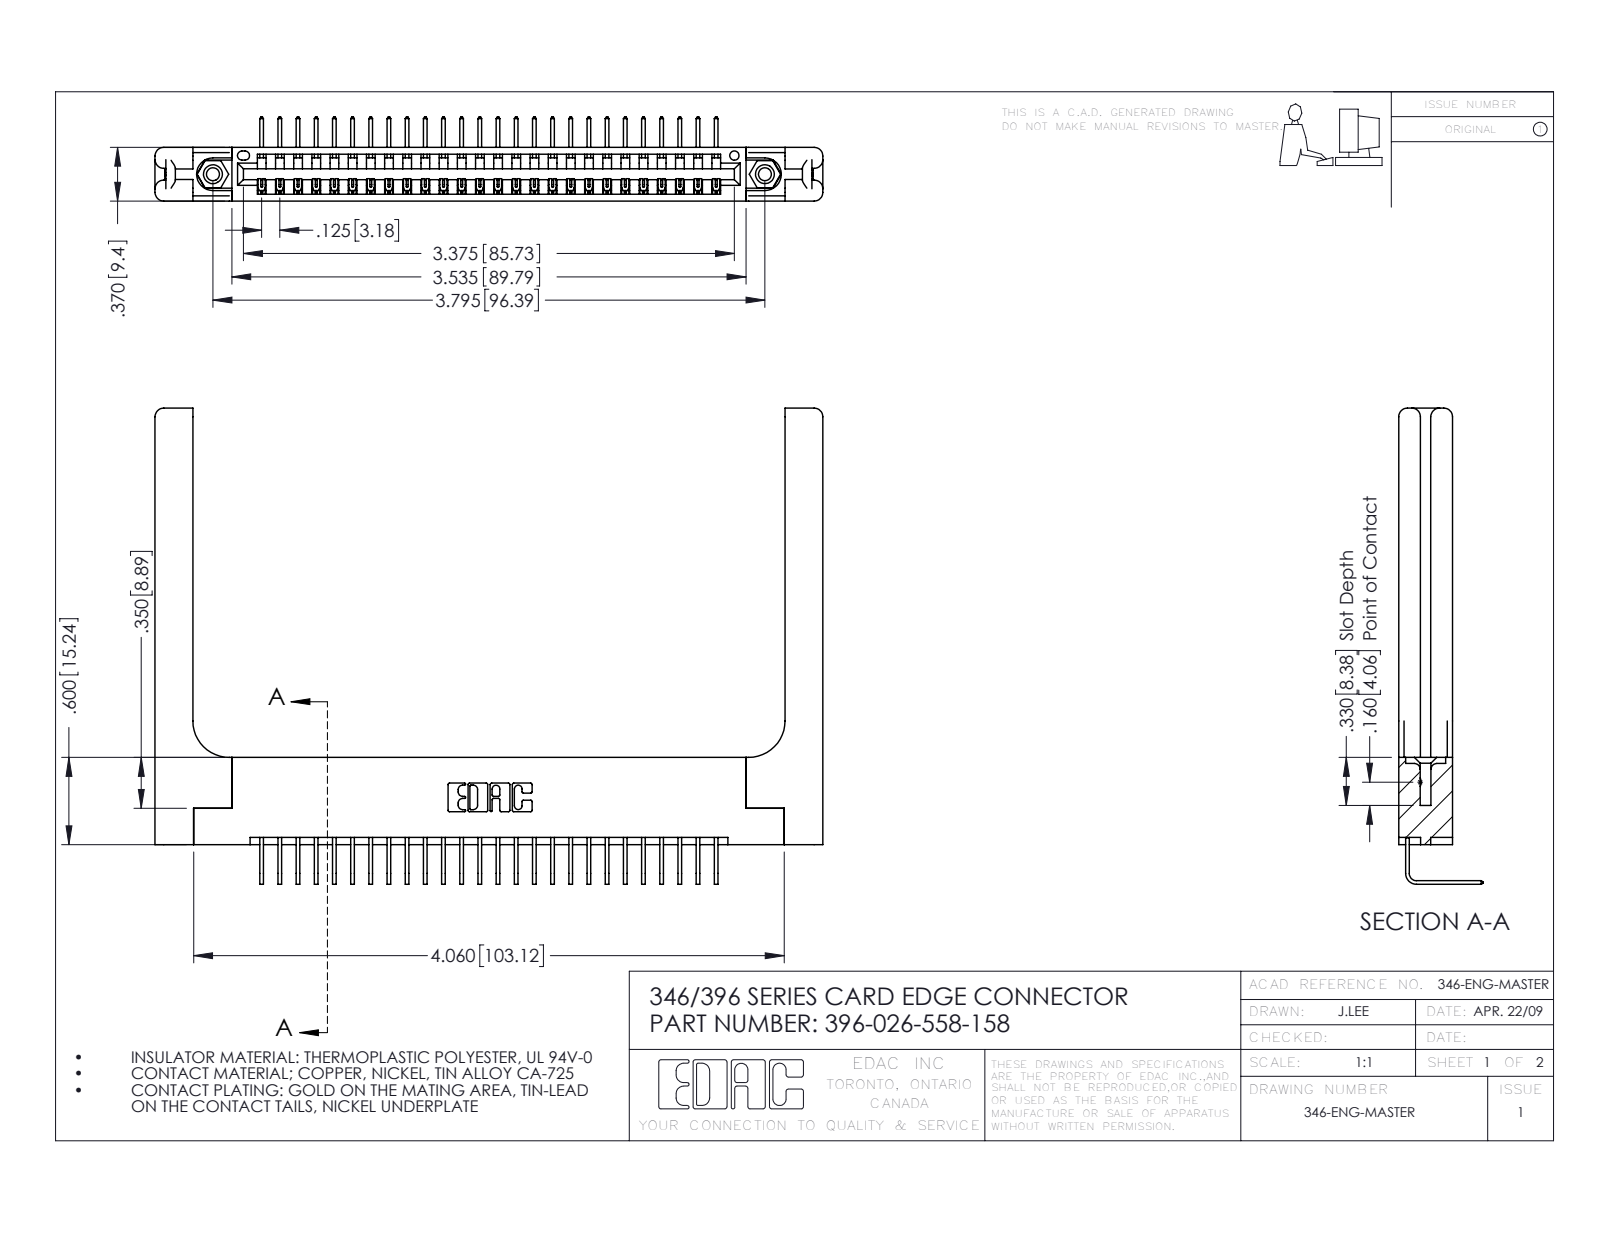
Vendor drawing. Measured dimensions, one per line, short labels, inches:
name: 346 Part_Flush Mounting Lugs - 0.156 Dia-TH; 396-026-558-158; 346-220-058_345-220-058; 345-250-001_345-250-001-102 (+1 more)
written by: SolidWorks 2016 (CONFIG_CONTROL_DESIGN)
unit: in
bodies: 31 solids, 1938 faces (1316 planar, 562 cylindrical, 60 other)
size: 4.591 × 3.273 × 0.58
volume: 1.139 in³; area: 30.13 in²
holes: 2× ⌀0.089, 2× ⌀0.125, 2× ⌀0.156, 1× ⌀0.064
bosses: 2× ⌀0.155
rounds: 52× R0.006, 22× R0.01, 16× R0.06, 6× R0.007, 6× R0.031, 3× R0.026, 2× R0.03, 2× R0.031
face distances: 0.37, 0.322, 0.072, 0.048, 0.148, 0.15, 0.25, 0.025, 0.298, 0.076
hole spacings: 0.246, 3.587, 3.795
